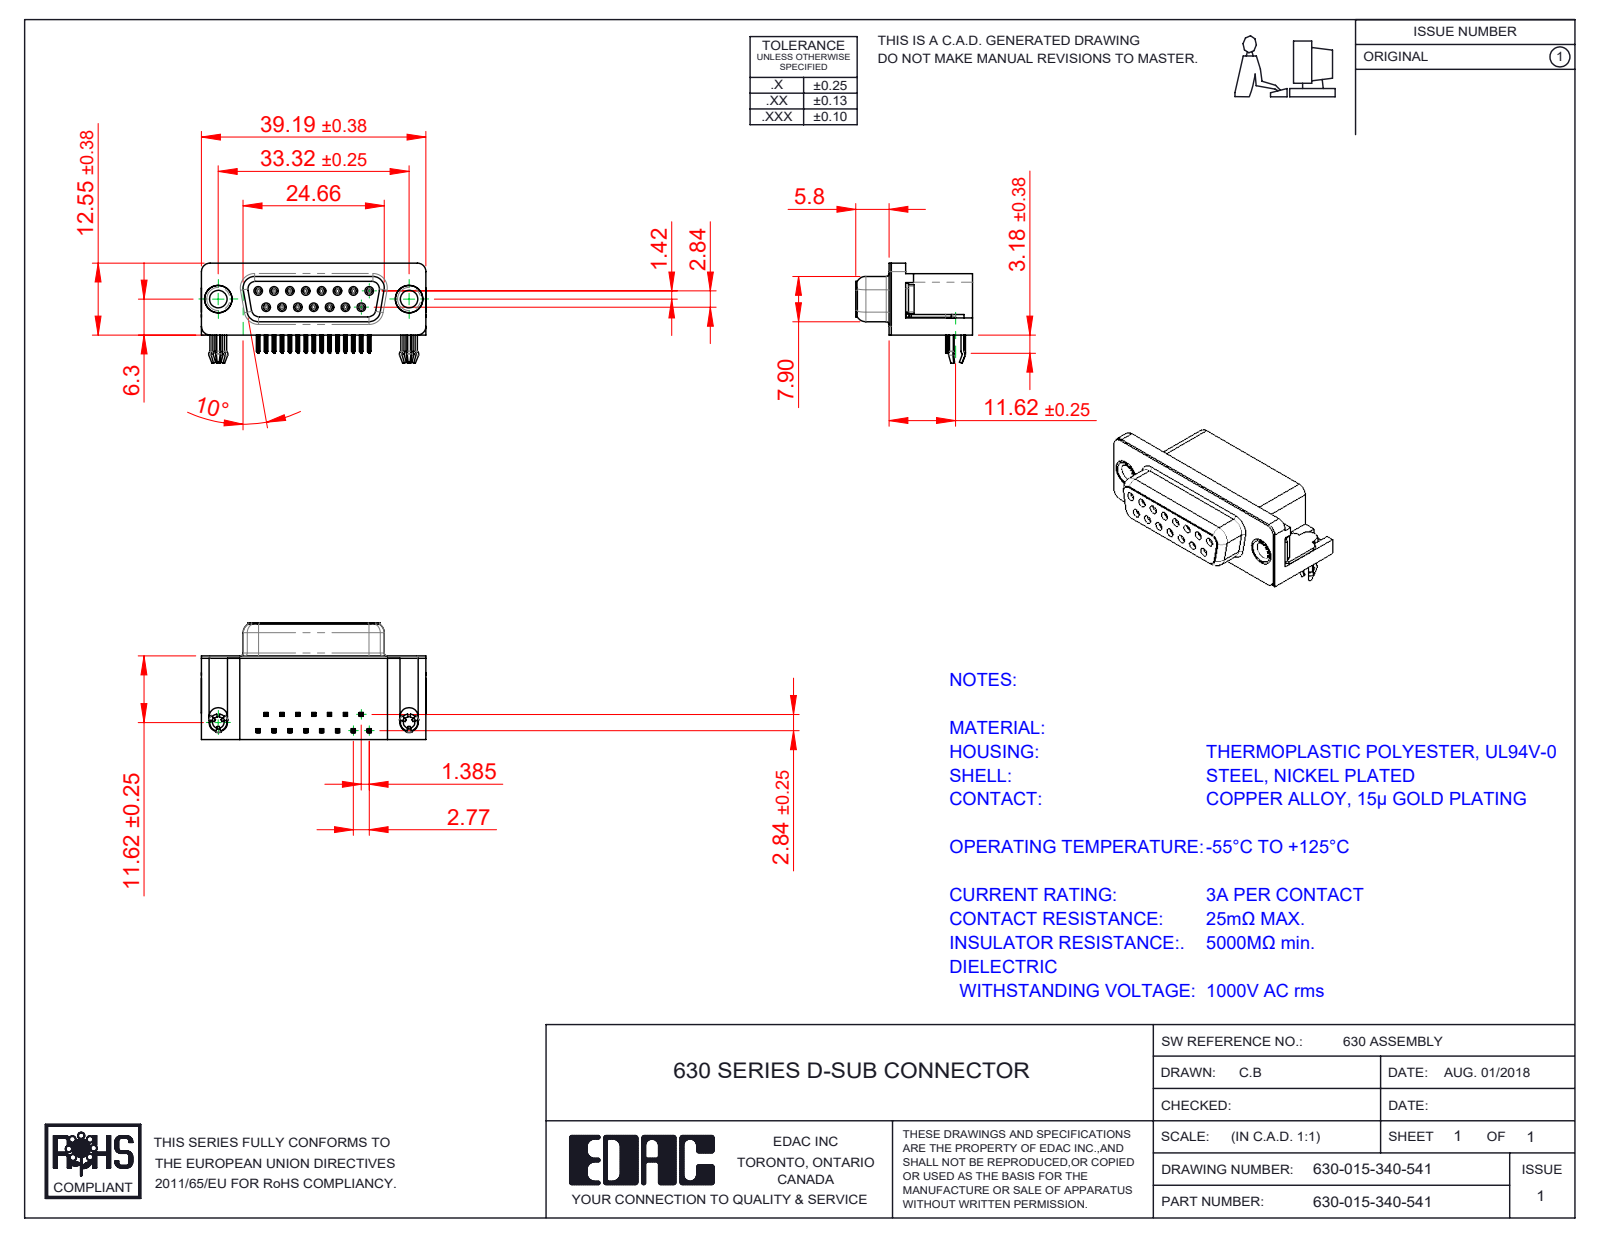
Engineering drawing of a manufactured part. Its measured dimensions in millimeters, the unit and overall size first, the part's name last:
Units: millimetres
Overall size (bounding box): 39.22 × 20.4 × 17.48
Round holes (diameter × count): ⌀0.8 ×15, ⌀0.9 ×15, ⌀2 ×2, ⌀3.05 ×2, ⌀4 ×2, ⌀4.8 ×2, ⌀5 ×2
Round bosses / shafts (diameter × count): ⌀1.2 ×15, ⌀4.9 ×2, ⌀4.75 ×2, ⌀3.85 ×2, ⌀3 ×2
Partial cylindrical surfaces — rounded edges, fillets, slot ends (radius × count): R0.1 ×120, R0.15 ×60, R0.35 ×30, R1 ×18, R0.34 ×15, R0.25 ×12, R1.35 ×8, R1.5 ×8
Main face-to-face distances: 0.4, 14.2, 6.2, 10.35, 2.73, 14.6, 2.9, 3.18, 6.65, 9.38
Hole centre spacings: 3.16, 2.77, 5.54, 5.03, 5.04, 7.48, 7.49, 8.31
Volume: 5 856 mm³ · Surface area: 7 236 mm²
Bodies: 21 solids, 2489 faces (1110 planar, 593 cylindrical, 786 other)
Part name (STEP PRODUCT): 630 3 Prong Board Lock; 630 Contact Bottom; 630 Housing_15 Socket; 630 Thru Hole Rivet (+3 more)
STEP written by: SolidWorks 2020 (CONFIG_CONTROL_DESIGN)
